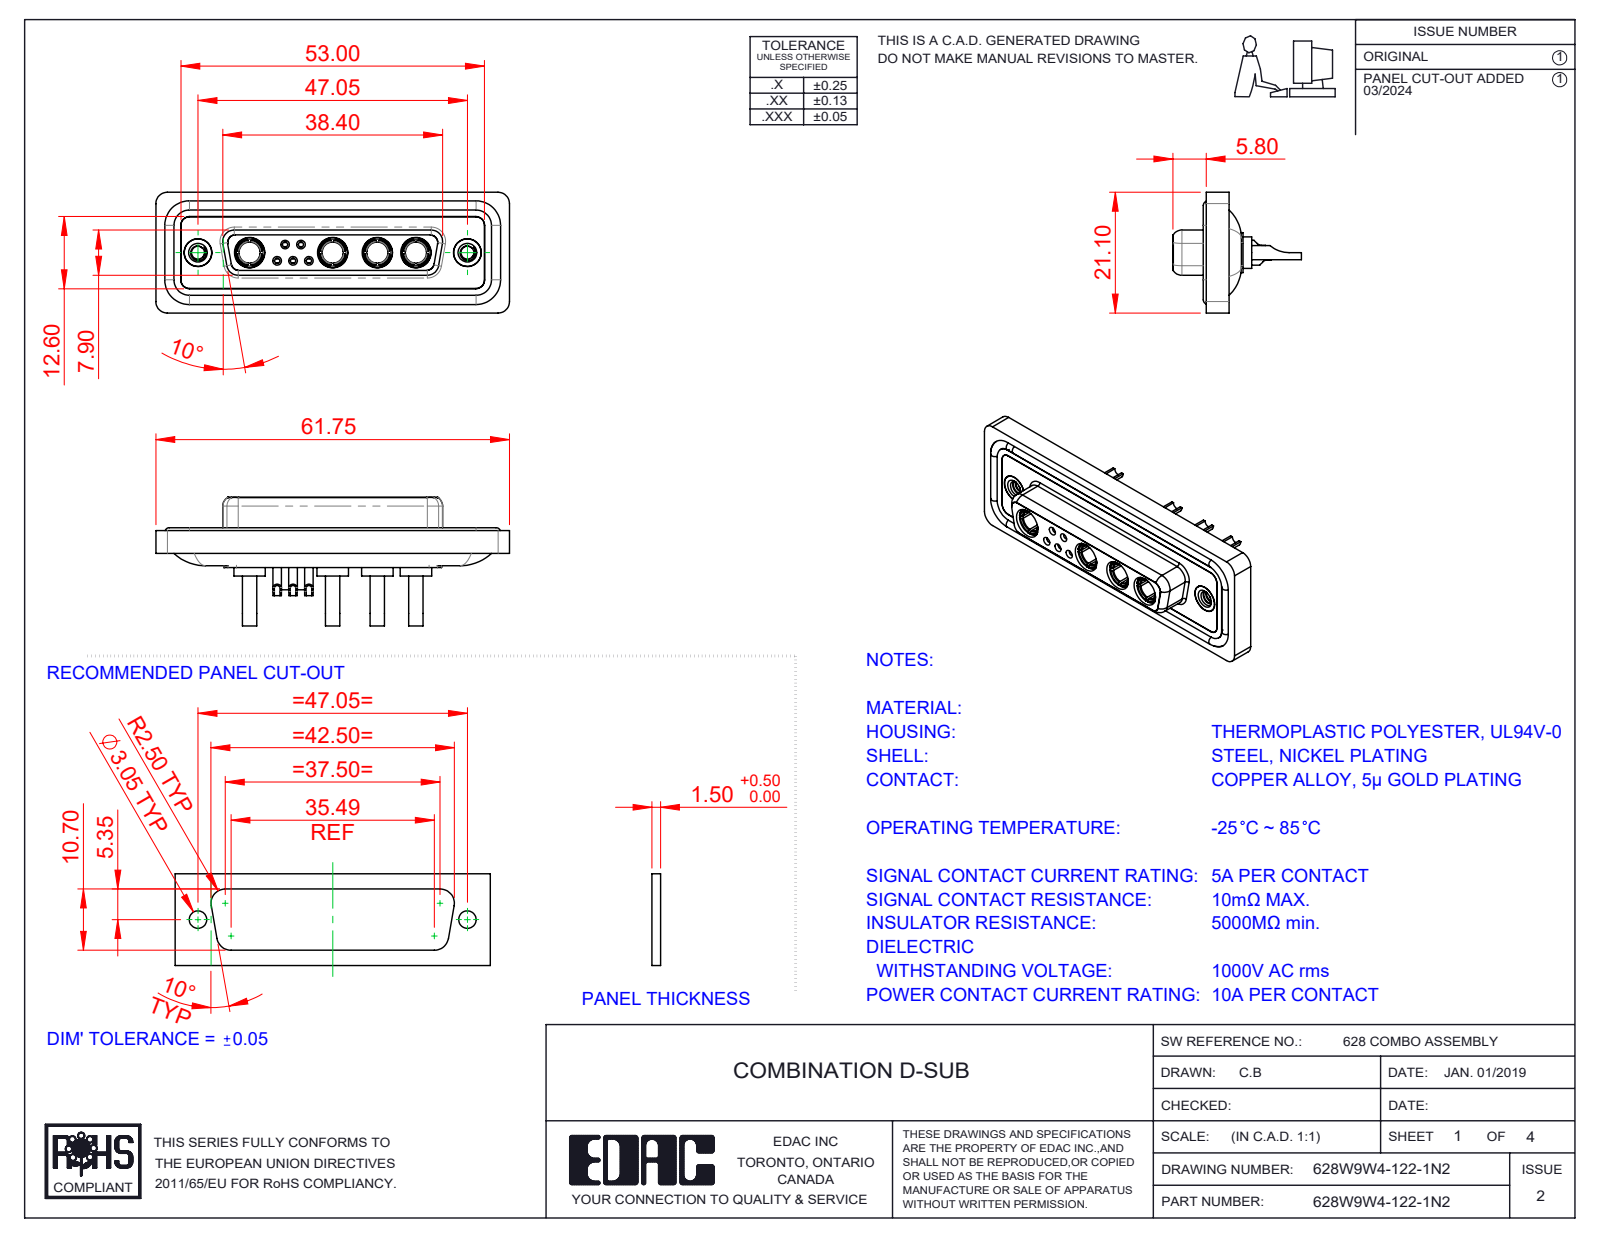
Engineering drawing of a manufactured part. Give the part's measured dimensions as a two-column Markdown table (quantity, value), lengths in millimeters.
| quantity | value |
| --- | --- |
| part name | 628Combo Threaded Rivet_2; 628Combo Contact Row 1_22; 628Combo Contact Row 2_22; 628Combo Waterproof Housing_25 Contacts (+5 more) |
| STEP written by | SolidWorks 2023 (CONFIG_CONTROL_DESIGN) |
| units | millimeters |
| bodies | 20 solids, 977 faces (314 planar, 397 cylindrical, 266 other) |
| overall size | 61.75 × 22.45 × 21.1 |
| volume | 8 223 mm³ |
| surface area | 13 808 mm² |
| round holes (diameter × count) | 4.85 × 6, 0.9 × 5, 1 × 5, 1.1 × 5, 1.5 × 5, 2 × 5, 1.7 × 4, 3.7 × 4, 5.3 × 4, 1.6 × 3, 1.7 × 2, 2.26 × 2 |
| round bosses / shafts (diameter × count) | 1.6 × 6, 2.2 × 5, 5.5 × 4, 5.2 × 4, 4.96 × 4, 4.75 × 4, 3.75 × 4, 2.5 × 4 |
| partial cylindrical surfaces (radius × count) | 1.5 × 22, 2 × 18, 1.35 × 8, 1.6 × 8, 1 × 6, 0.25 × 4, 0.5 × 4, 0.6 × 4 |
| main face-to-face distances | 0.4, 1.8, 7.45, 5.65, 0.5, 7.05, 6.6, 1.6, 1.1, 2.9 |
| hole center spacings | 3.16, 2.77, 5.03, 2.76, 4.4, 5.02, 5.54, 5.73 |
